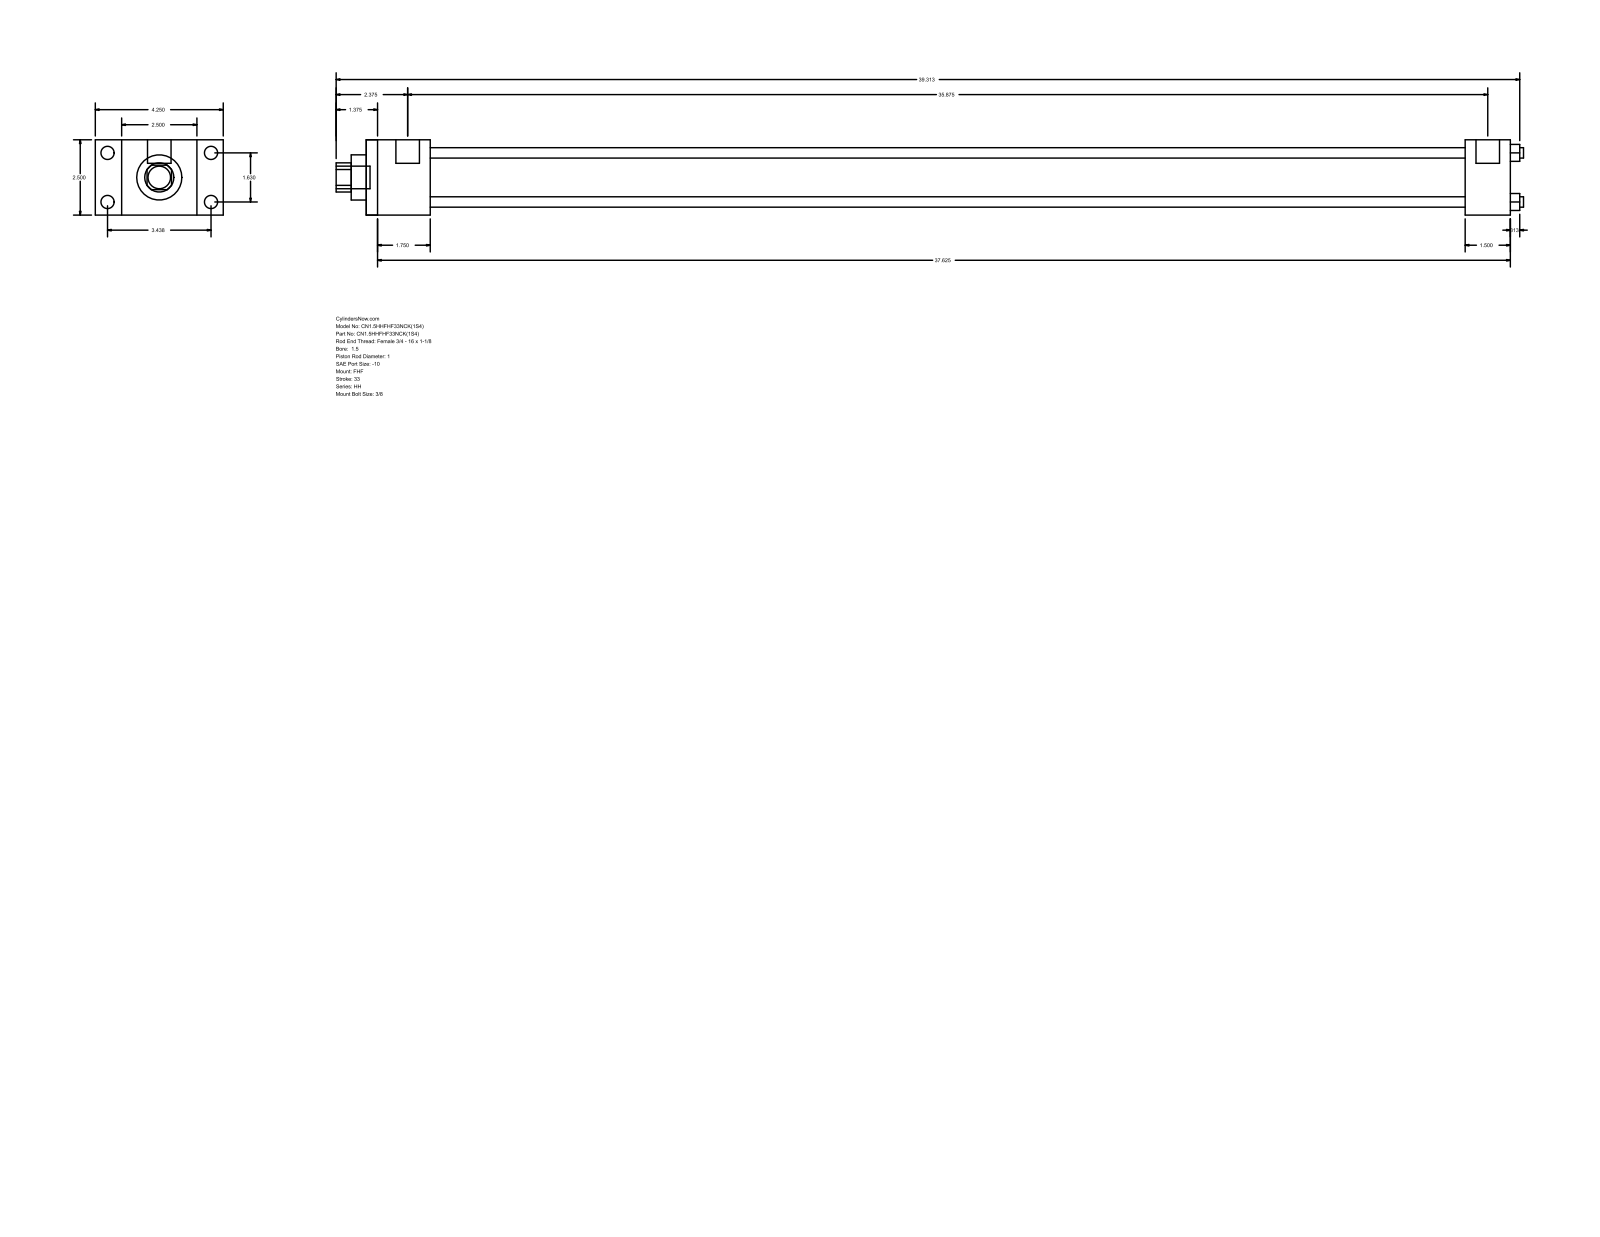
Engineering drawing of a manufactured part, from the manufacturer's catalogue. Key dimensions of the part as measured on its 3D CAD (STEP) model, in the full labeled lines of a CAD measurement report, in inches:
Part name (STEP PRODUCT): HH_FHF__0150_1
STEP written by: GSSL Pune (CONFIG_CONTROL_DESIGN)
Units: inches
Bodies: 0 solids, 88 faces (60 planar, 28 cylindrical, 0 other)
Overall size (bounding box): 39.437 × 4.25 × 2.5
Round holes (diameter × count): ⌀0.345 ×4, ⌀1 ×1, ⌀1.5 ×1, ⌀1.75 ×1
Round bosses / shafts (diameter × count): ⌀0.438 ×4, ⌀0.219 ×4, ⌀0.781 ×2, ⌀0.75 ×1
Partial cylindrical surfaces — rounded edges, fillets, slot ends (radius × count): R0.484 ×1
Main face-to-face distances: 2.5, 0.875, 3.375, 2.125, 4.25, 38, 35.875, 36.5, 34.375, 1.5
Hole centre spacings: 1.152, 1.63, 2.305
